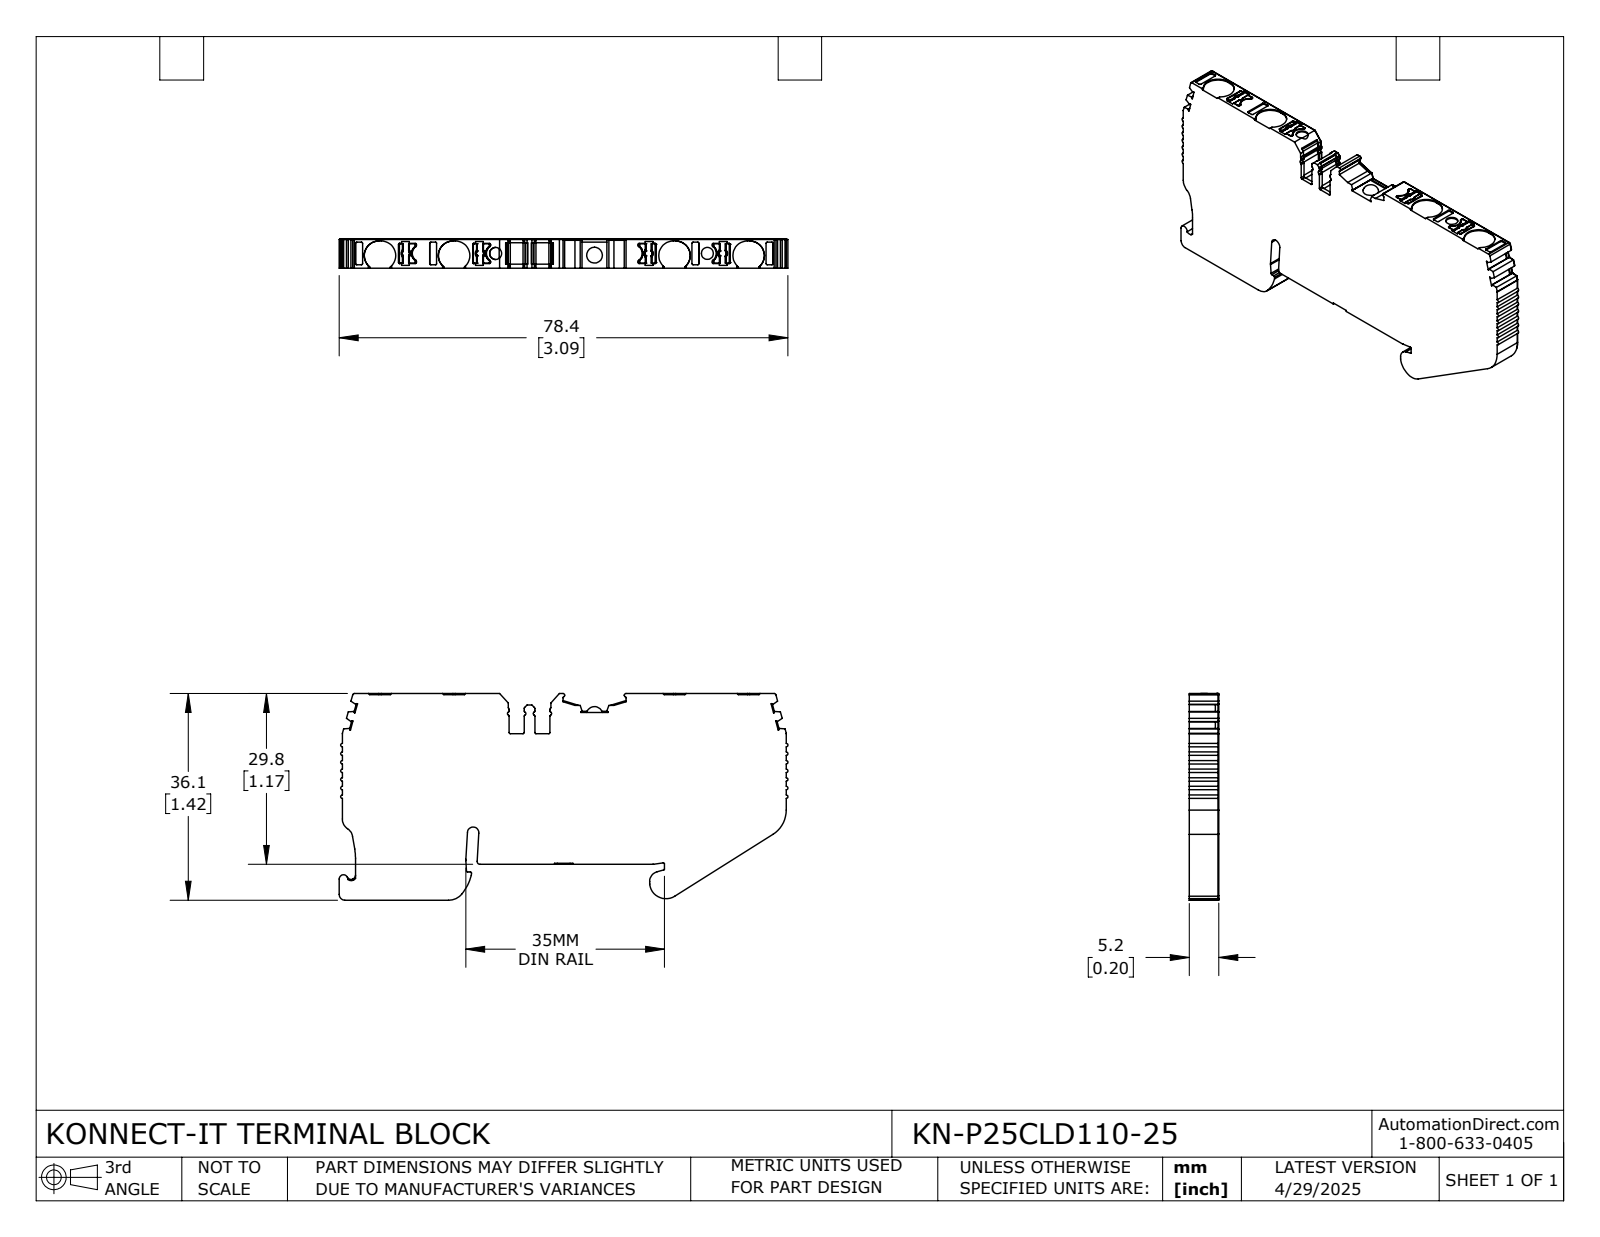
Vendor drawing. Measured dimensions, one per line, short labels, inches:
name: KN-P25CLD110-25
written by: SolidWorks 2024 (CONFIG_CONTROL_DESIGN)
unit: in
bodies: 1 solid, 744 faces (381 planar, 291 cylindrical, 72 other)
size: 3.085 × 1.42 × 0.203
volume: 0.731 in³; area: 9.642 in²
holes: 2× ⌀0.083
rounds: 78× R0.008, 39× R0.012, 21× R0.004, 18× R0.02, 16× R0.006, 9× R0.016, 8× R0.1, 4× R0.059
face distances: 0.203, 1.166, 1.174, 0.246, 1.412, 1.42, 3.052, 0.047, 0.197, 0.177
hole spacings: 1.456
